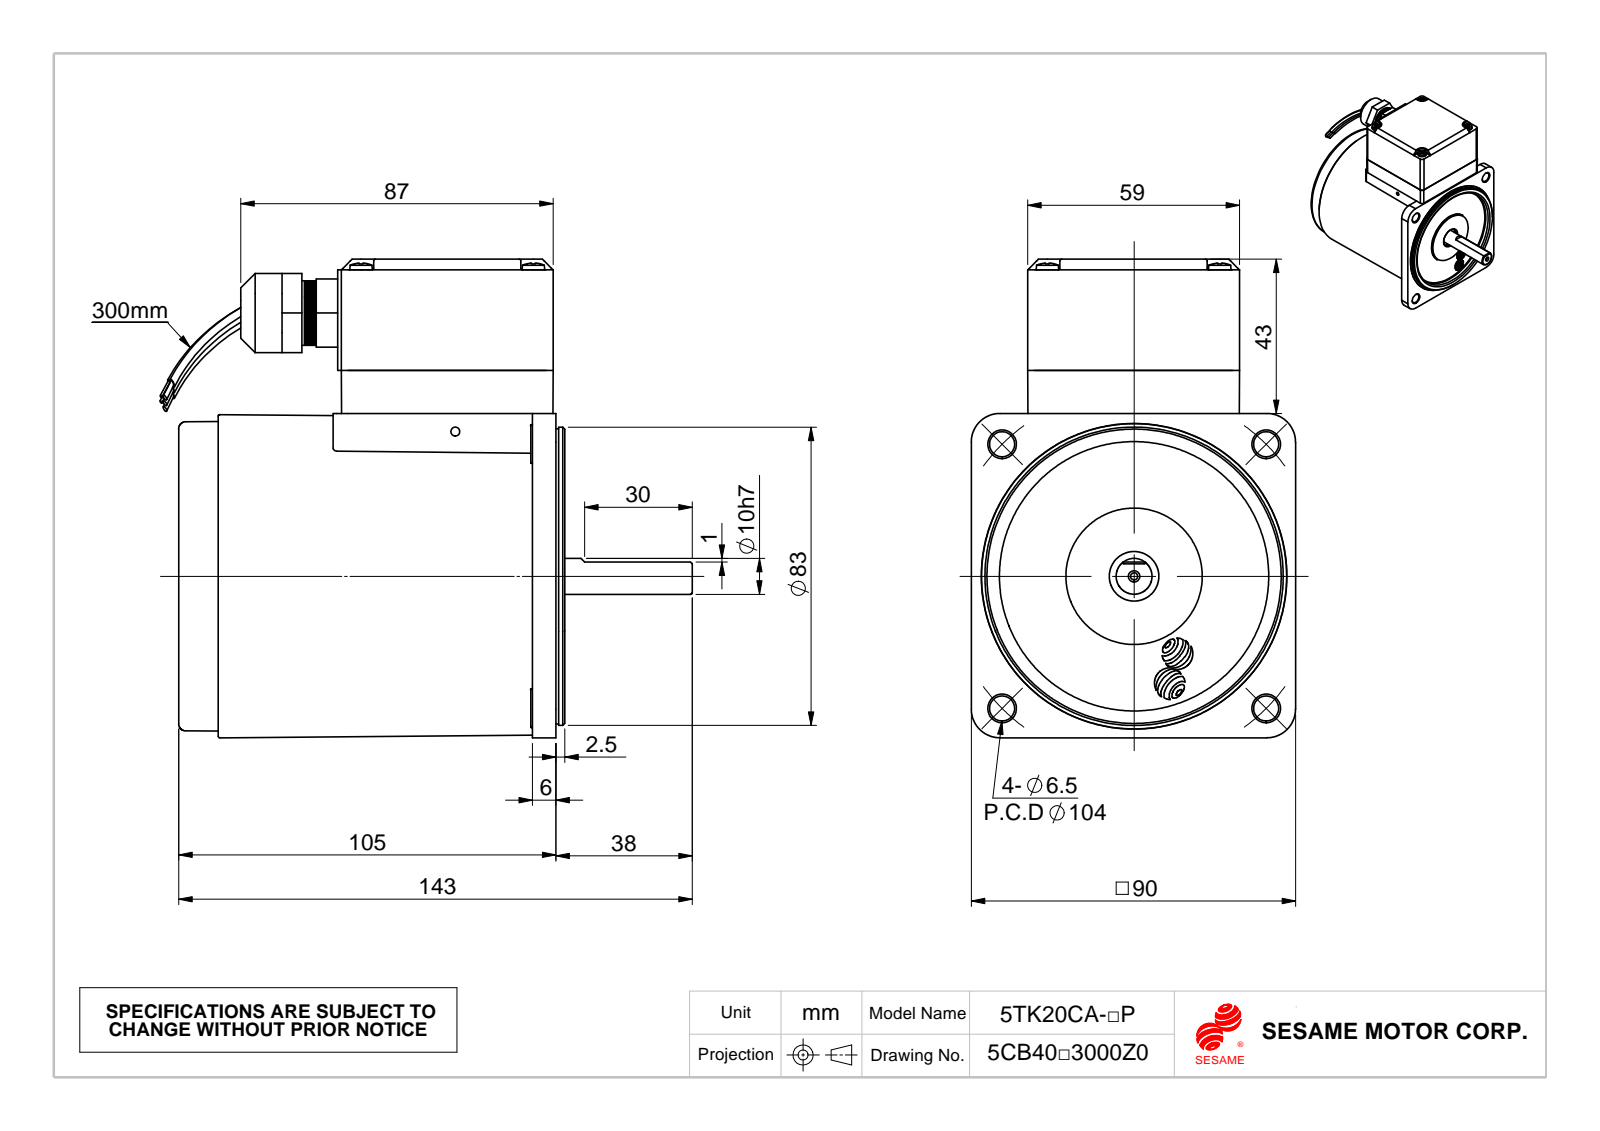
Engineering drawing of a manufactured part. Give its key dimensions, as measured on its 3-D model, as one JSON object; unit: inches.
{"part_name": "Ts下墊片; M540Ts; 成品180度; 40A", "step_written_by": "SolidWorks 2010 (CONFIG_CONTROL_DESIGN)", "units": "inches", "bodies": {"solids": 14, "faces": 2581, "planar": 226, "cylindrical": 936, "other": 1419}, "overall_size": [5.835, 5.248, 3.555], "volume_in3": 20.86, "surface_area_in2": 200.5, "round_holes": [[0.13, 4], [0.138, 4], [0.154, 4], [0.169, 4], [0.276, 4], [0.079, 1], [0.098, 1], [0.433, 1], [0.472, 1], [0.539, 1], [0.571, 1], [0.827, 1]], "round_bosses_or_shafts": [[0.248, 4], [0.118, 4], [0.394, 2], [3.316, 1], [3.268, 1], [3.236, 1], [1.496, 1], [1.378, 1]], "partial_cylinders_radius": [[0.079, 12], [0.02, 8], [0.031, 8], [0.059, 8], [0.065, 8], [0.115, 8], [0.157, 8], [0.008, 4]], "face_to_face_distances": [0.472, 0.039, 3.606, 4.075, 0.059, 3.898, 0.291, 0.03, 0.138, 1.693], "hole_center_spacings": [1.89, 2.047, 2.895, 0.459, 0.486, 0.5, 0.981, 0.984]}
